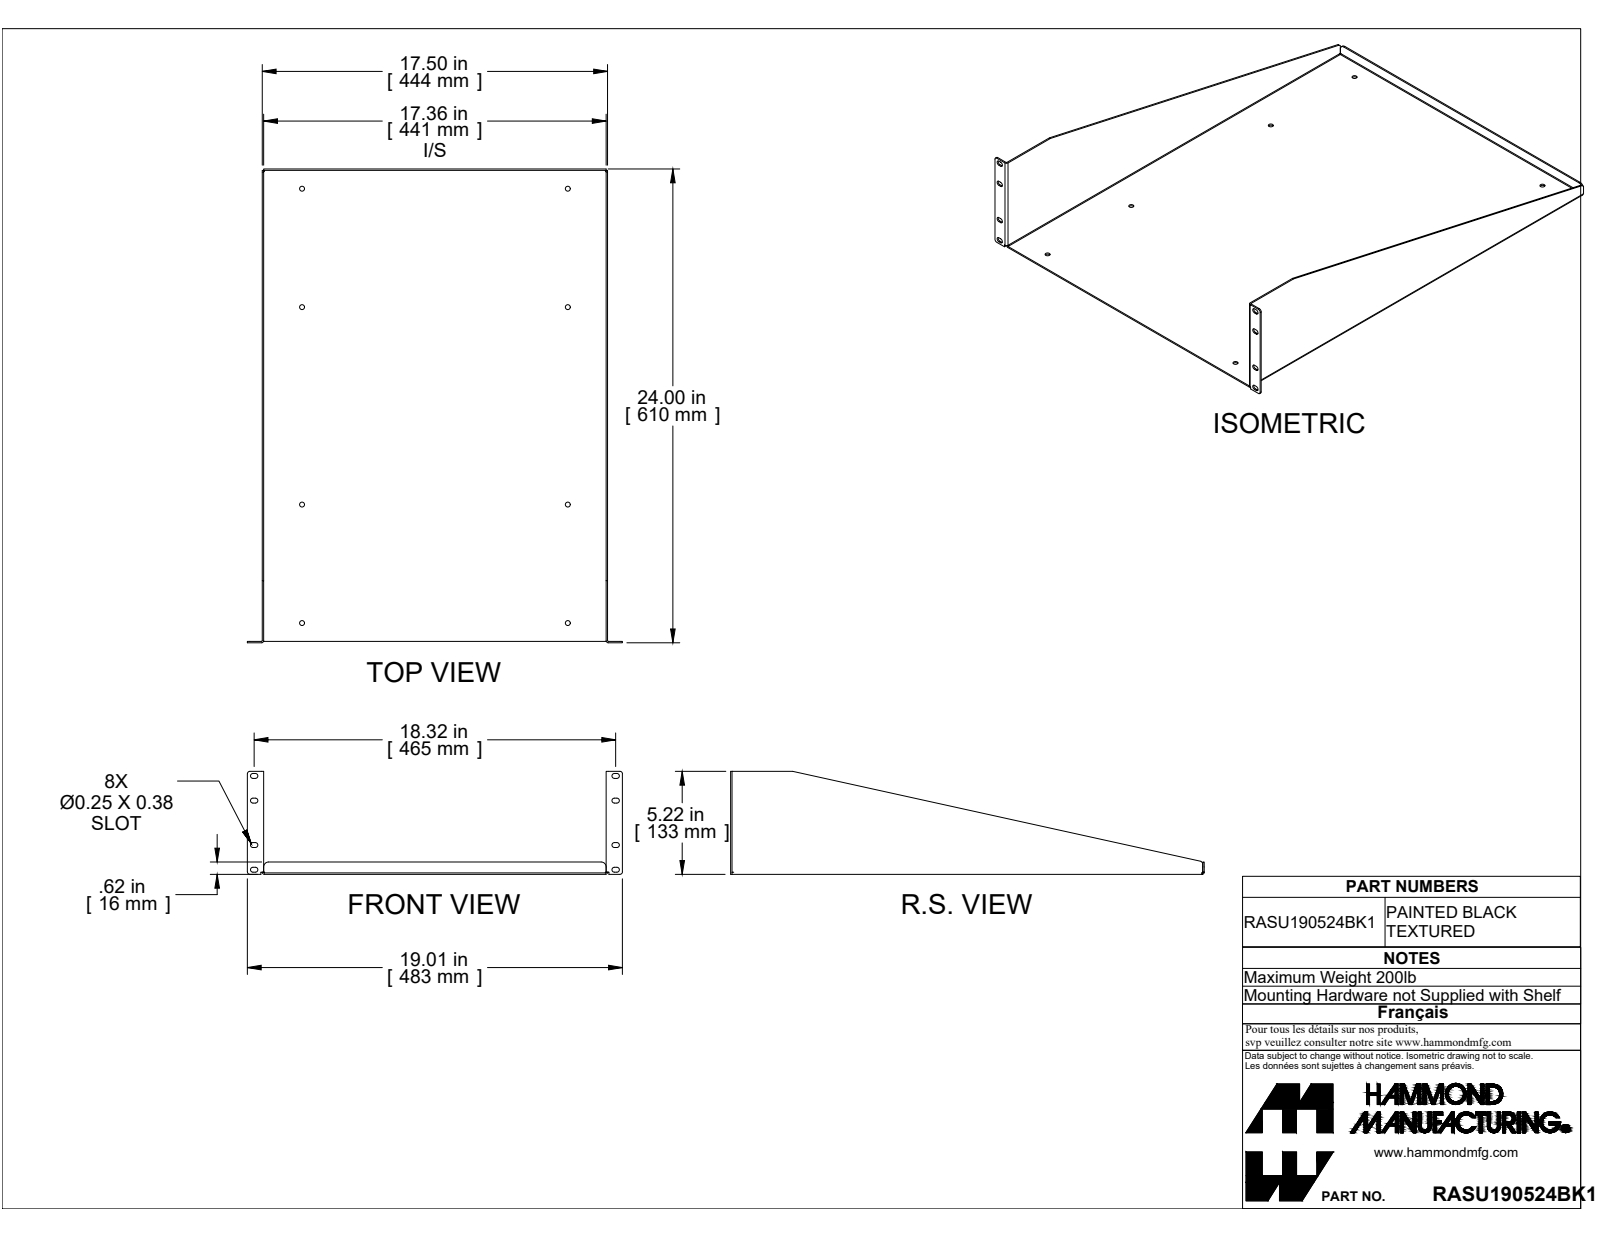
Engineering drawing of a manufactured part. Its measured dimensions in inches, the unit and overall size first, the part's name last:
Units: inches
Overall size (bounding box): 24 × 19.006 × 5.218
Round holes (diameter × count): ⌀0.25 ×8
Partial cylindrical surfaces — rounded edges, fillets, slot ends (radius × count): R0.125 ×20, R0.036 ×5, R0.108 ×5, R0.055 ×3, R0.25 ×2
Main face-to-face distances: 0.072, 17.428, 17.356, 17.5, 23.856, 23.928, 0.072, 23.928, 24, 0.625
Hole centre spacings: 6, 13.468, 14.744, 16, 20.914, 10, 16.774, 22
Volume: 42.04 in³ · Surface area: 1 176 in²
Bodies: 1 solid, 104 faces (56 planar, 44 cylindrical, 4 other)
Part name (STEP PRODUCT): RASU190524BK1
STEP written by: SolidWorks 2019 (CONFIG_CONTROL_DESIGN)
